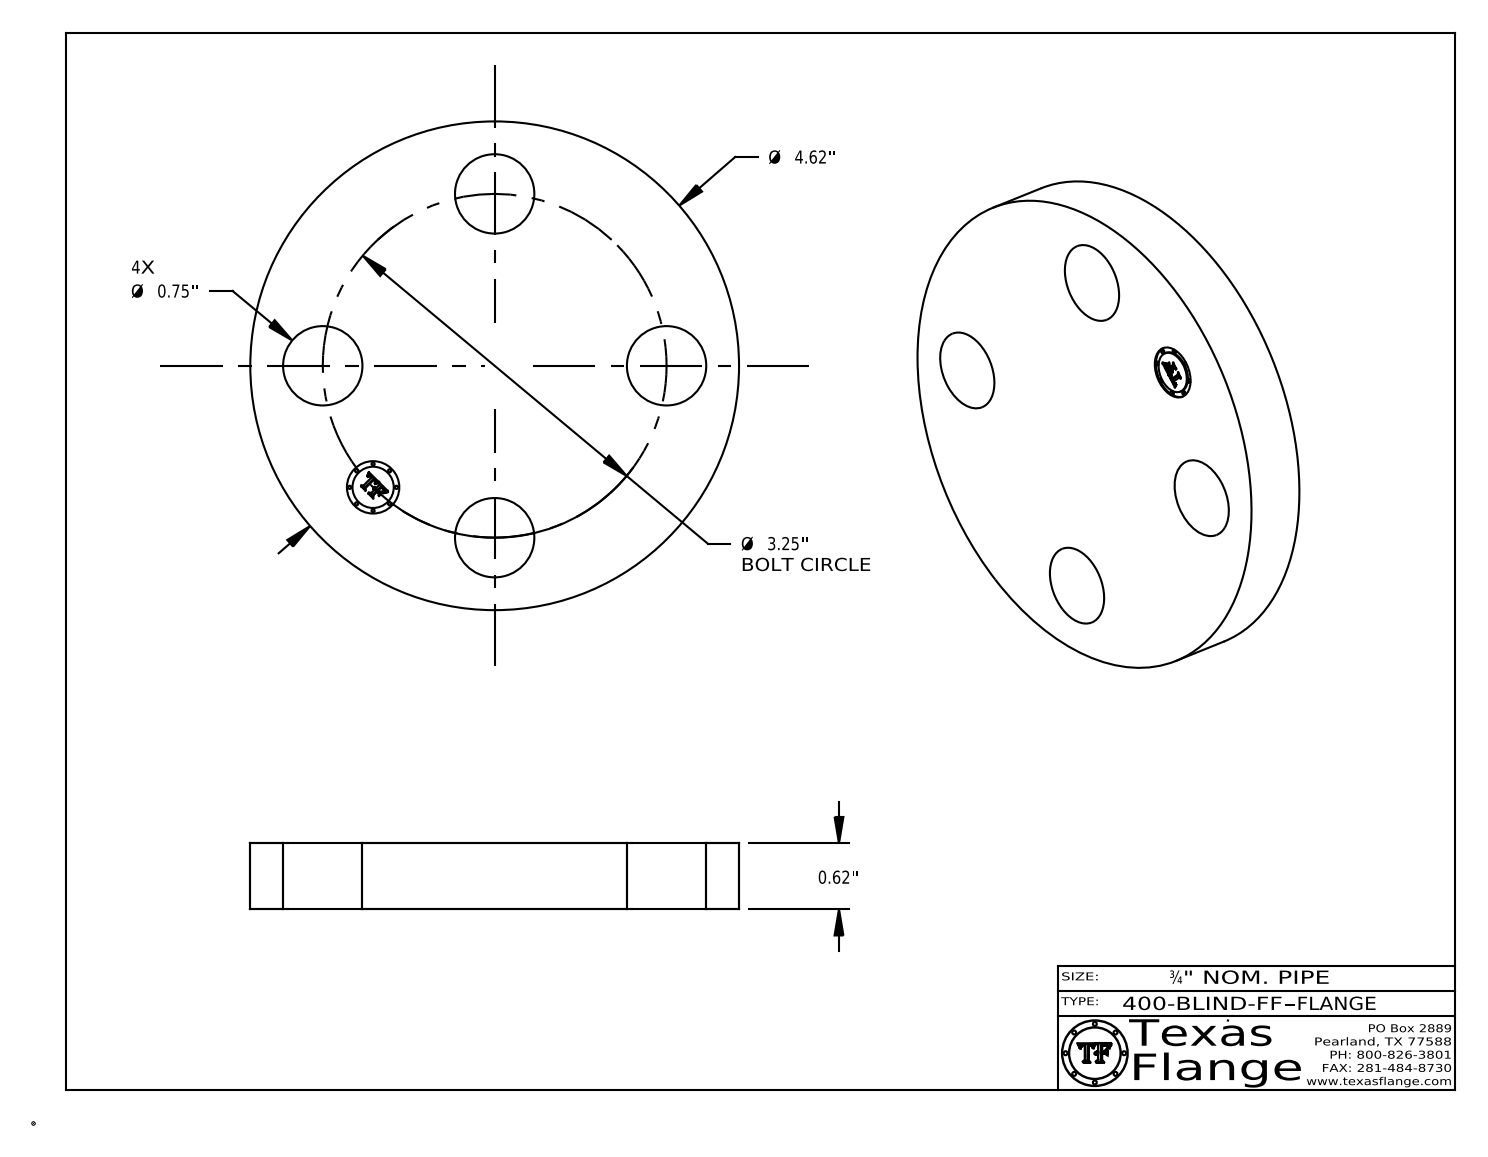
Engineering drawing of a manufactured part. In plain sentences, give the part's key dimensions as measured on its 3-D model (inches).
The part is named "400-BLIND-FF". Its 3-D file was written by "CATIA V5 STEP AP214 (AUTOMOTIVE_DESIGN)". It is 1 solid with 397 faces: 367 planar, 30 cylindrical and 0 other. Overall it measures 4.62 by 4.62 by 0.62 inches. Its volume is 9.297 cubic inches and its surface area 44.93 square inches. Round holes: 4 of diameter 0.75, 1 of diameter 0.495. Round bosses or shafts: 8 of diameter 0.03, 1 of diameter 4.62, 1 of diameter 0.39. The main face-to-face distances are 0.62, 0.605, 0.015, 0.148, 0.144, 0.027, 0.096, 0.122, 0.021, 0.074. The hole center spacings are 2.298, 1.244, 3.003, 3.25.
